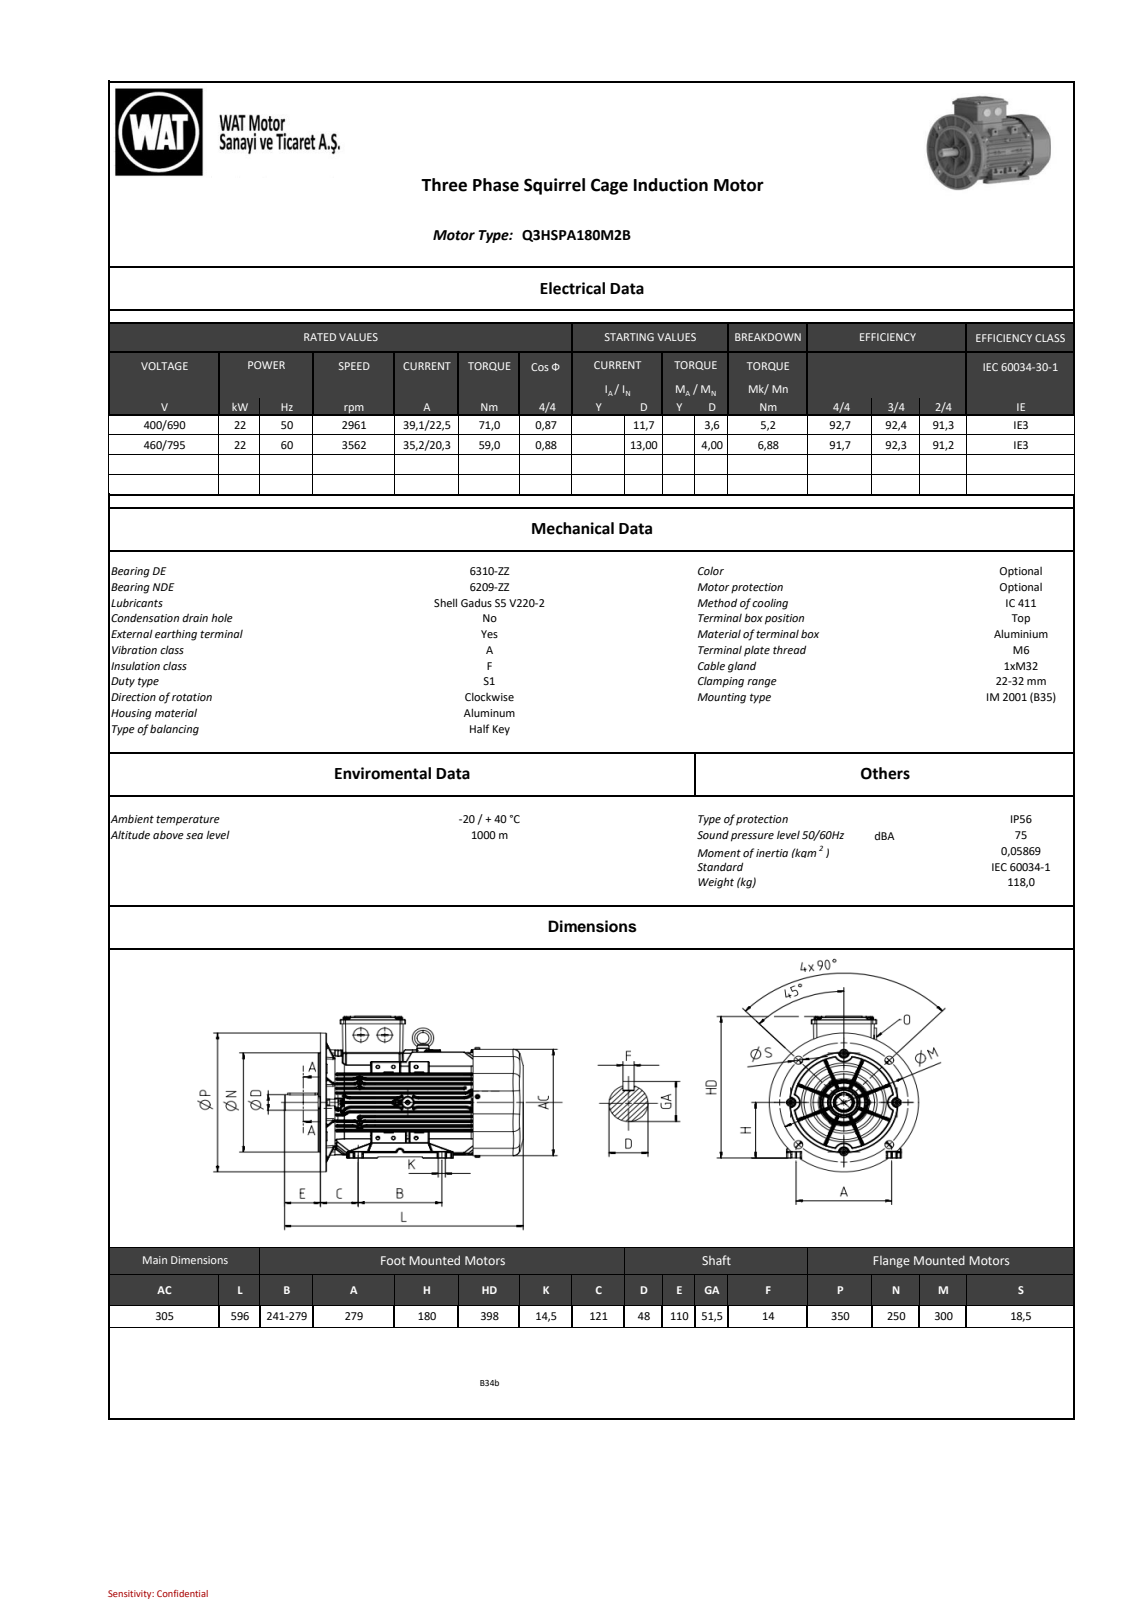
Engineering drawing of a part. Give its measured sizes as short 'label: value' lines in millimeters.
name: 001_objects
written by: SIEMENS PLM Software NX2206.8101 (AP203_CONFIGURATION_CONTROLLED_3D_DESIGN_OF_MECHANICAL_PARTS_AND_ASSEMBLIES_MIM_LF)
unit: mm
bodies: 0 solids, 7914 faces (1807 planar, 3359 cylindrical, 2748 other)
size: 595.97 × 398.75 × 349.89
holes: 5× ⌀17, 1× ⌀10, 1× ⌀16, 1× ⌀34.2, 1× ⌀72, 1× ⌀80, 1× ⌀85.63, 1× ⌀94, 1× ⌀114, 1× ⌀134, 1× ⌀154, 1× ⌀174
bosses: 4× ⌀8, 2× ⌀38, 1× ⌀272.5, 1× ⌀250, 1× ⌀178, 1× ⌀168, 1× ⌀158, 1× ⌀138
rounds: 694× R0.5, 499× R1, 385× R2, 89× R3, 78× R4, 66× R2.5, 54× R5, 16× R5.5
face distances: 11.85, 165.47, 144, 168, 9.32, 2.53, 156.15, 11.92, 1.5, 21.47
hole spacings: 142.5, 201.53, 142.31, 142.34, 142.66, 142.69, 285, 142.3
